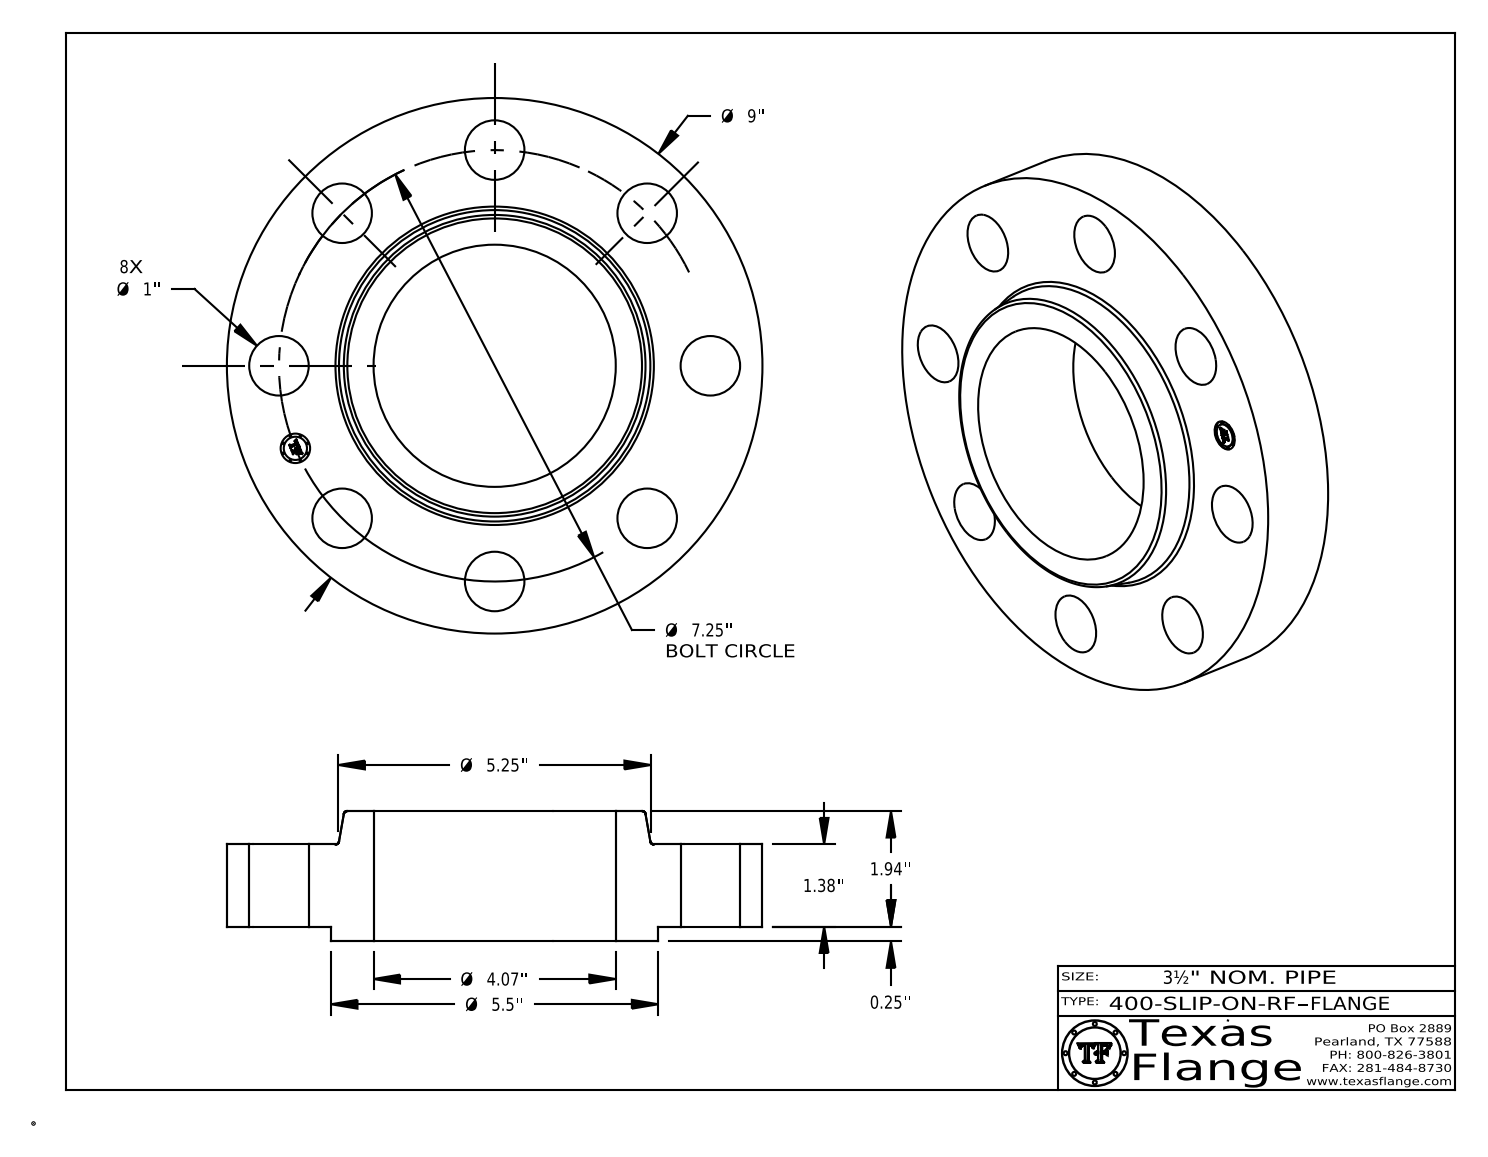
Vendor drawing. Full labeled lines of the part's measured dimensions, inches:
Part name (STEP PRODUCT): 400-SLIP-ON-RF
STEP written by: CATIA V5 STEP AP214 (AUTOMOTIVE_DESIGN)
Units: inches
Bodies: 1 solid, 417 faces (369 planar, 42 cylindrical, 6 other)
Overall size (bounding box): 9 × 9 × 2.19
Volume: 68.24 in³ · Surface area: 201.8 in²
Round holes (diameter × count): ⌀1 ×8, ⌀0.495 ×1, ⌀4.07 ×1
Round bosses / shafts (diameter × count): ⌀0.03 ×8, ⌀9 ×1, ⌀5.5 ×1, ⌀0.39 ×1
Main face-to-face distances: 1.38, 0.25, 1.63, 2.19, 1.94, 0.56, 1.615, 1.365, 0.015, 0.575
Hole centre spacings: 3.625, 2.774, 5.127, 6.698, 7.25, 1.415, 7.111, 4.028
